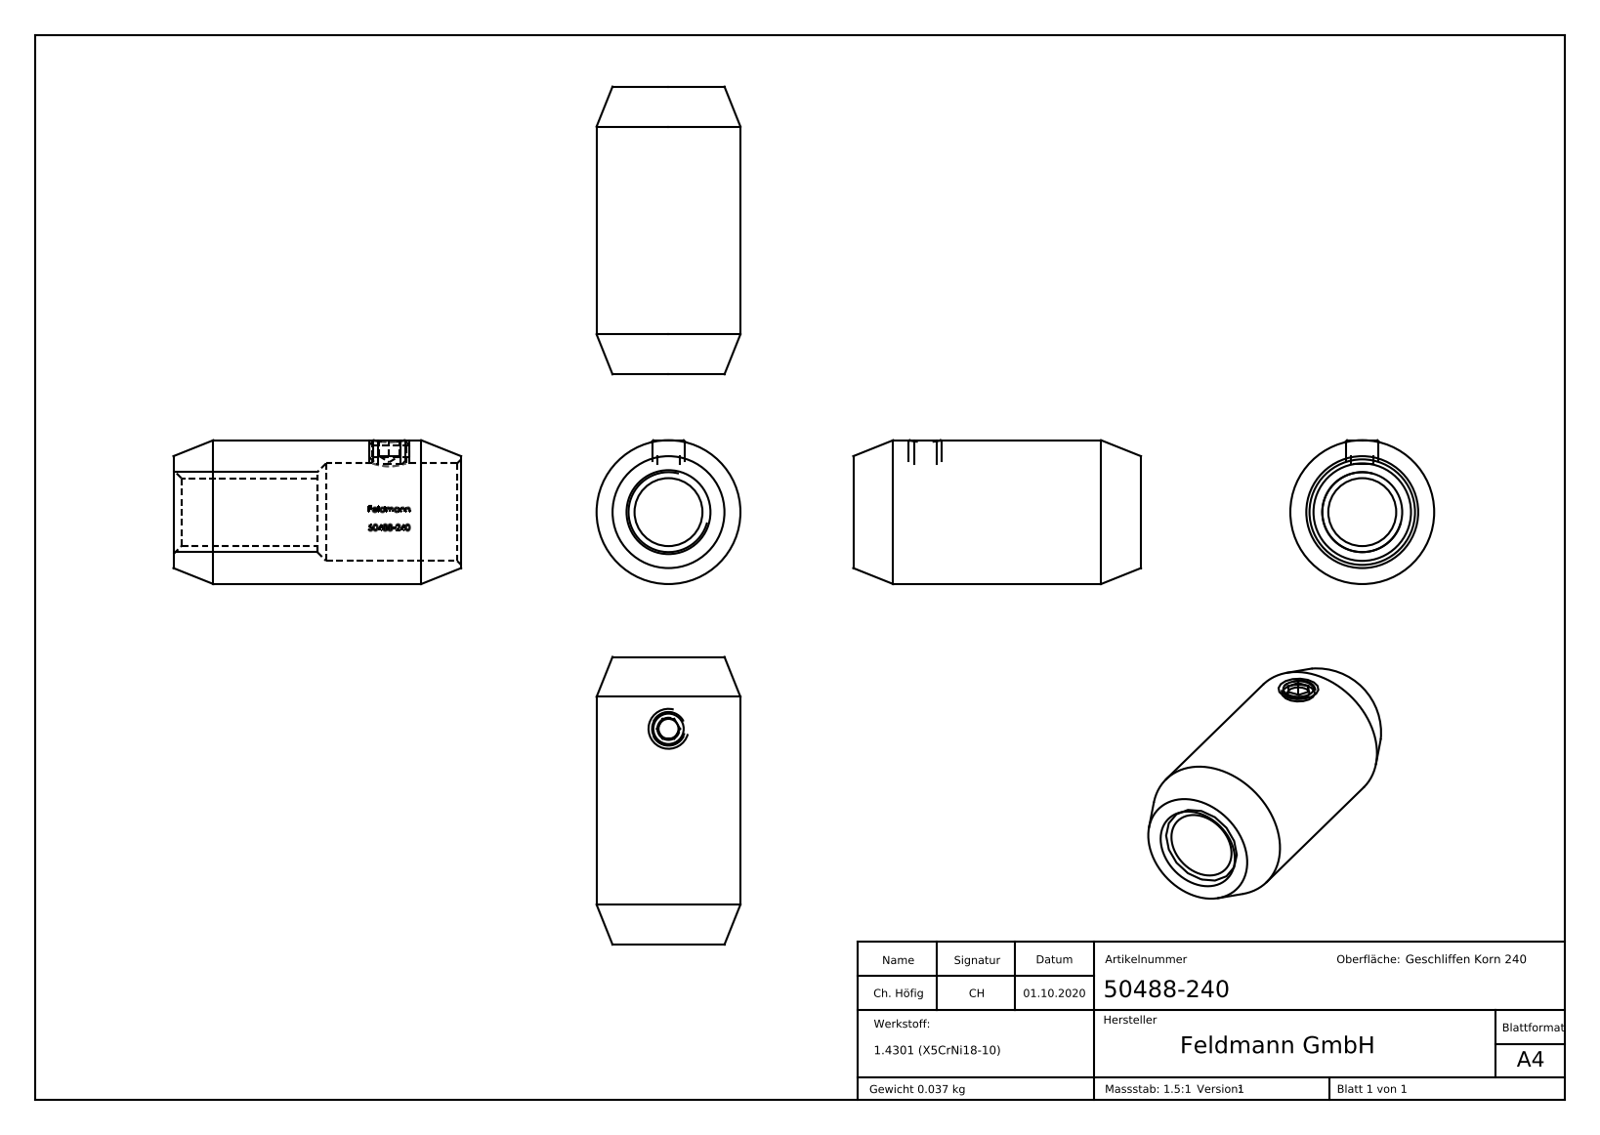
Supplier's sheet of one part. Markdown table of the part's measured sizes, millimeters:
| quantity | value |
| --- | --- |
| part name | 5048X-240 Teil1_50488-240 Teil1; 50488-240; DIN913; 5048X-240 Teil1 (+1 more) |
| STEP written by | SolidWorks 2018 (CONFIG_CONTROL_DESIGN) |
| units | millimeters |
| bodies | 2 solids, 281 faces (113 planar, 38 cylindrical, 130 other) |
| overall size | 70 × 36 × 18 |
| volume | 5 512 mm³ |
| surface area | 3 432 mm² |
| round holes (diameter × count) | 4.2 × 1, 8.5 × 1, 12.2 × 1 |
| round bosses / shafts (diameter × count) | 18 × 1, 5 × 1 |
| partial cylindrical surfaces (radius × count) | 6.2 × 1 |
| main face-to-face distances | 18, 36, 2.5, 3, 7.75, 10.25, 28.25, 25.75, 2, 1 |
